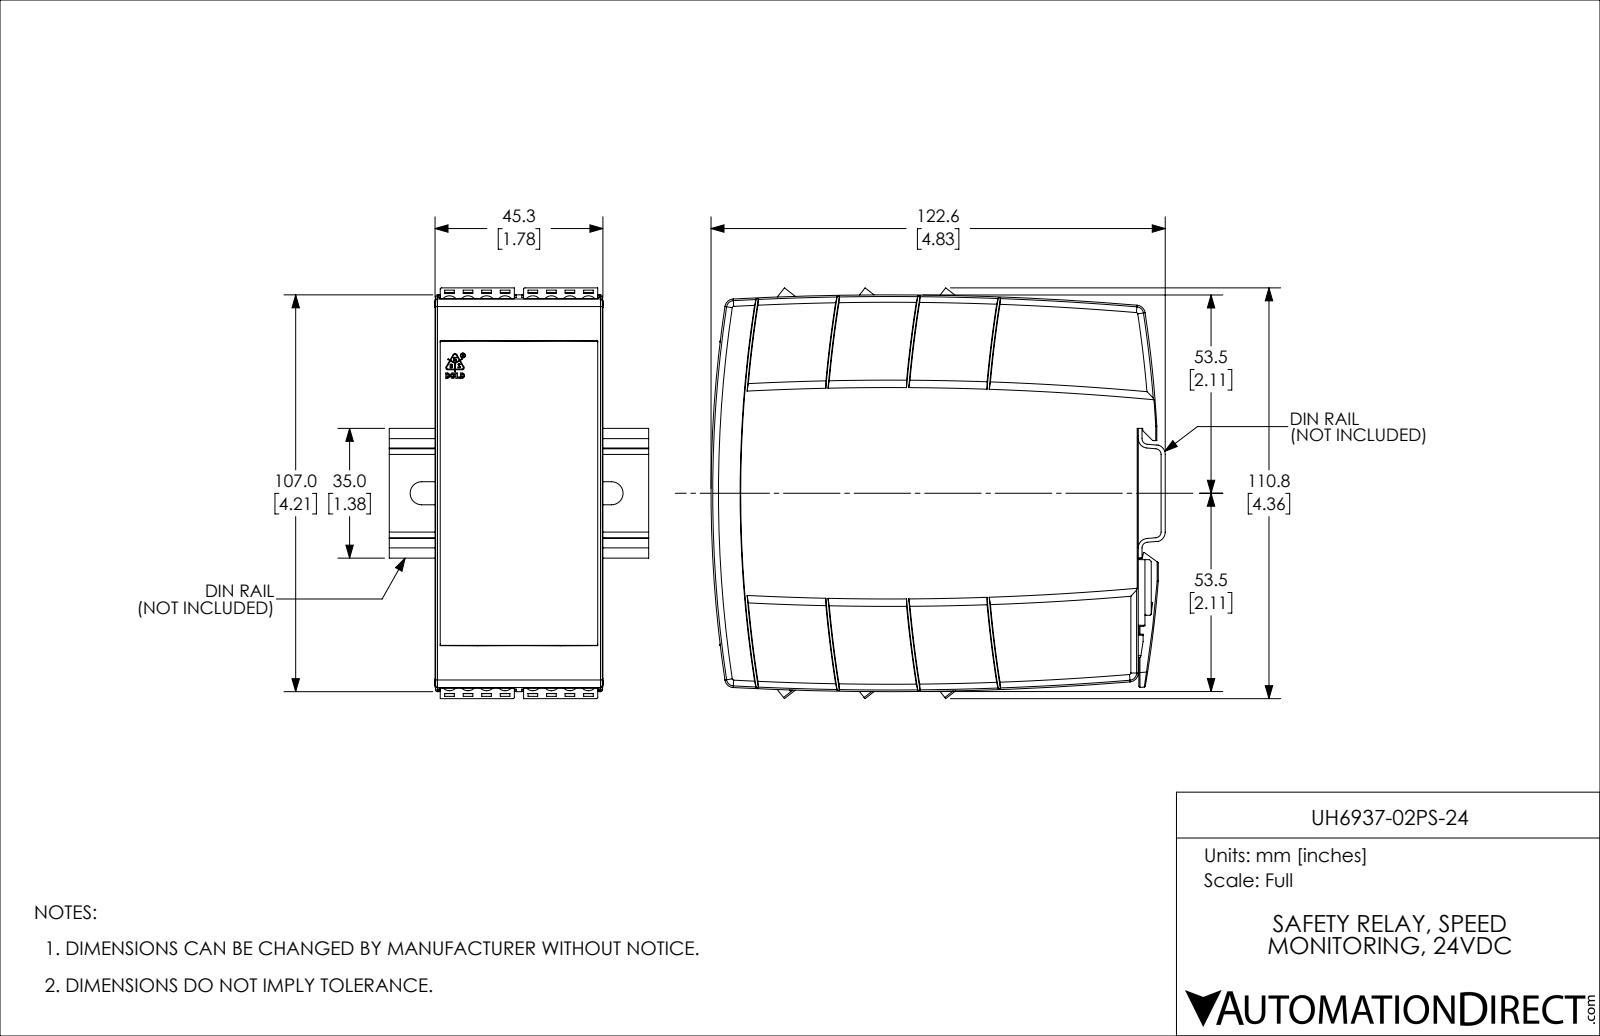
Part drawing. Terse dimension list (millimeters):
name: UH6937-02PS-24
written by: SolidWorks 2018 (AUTOMOTIVE_DESIGN)
unit: mm
bodies: 17 solids, 9587 faces (7538 planar, 1783 cylindrical, 266 other)
size: 120.7 × 110.8 × 45.3
volume: 108 100 mm³; area: 122 800 mm²
holes: 48× ⌀1.5, 48× ⌀3.2, 48× ⌀4, 6× ⌀0.7, 6× ⌀0.8, 1× ⌀1.2
bosses: 48× ⌀3.8, 6× ⌀2, 1× ⌀1.3
rounds: 48× R2.9, 37× R0.4, 18× R0.1, 18× R0.3, 18× R0.3, 18× R0.3, 12× R0.1, 12× R0.2
face distances: 1.1, 43.7, 42.6, 1.3, 43.9, 45.1, 17.1, 22.5, 44.9, 2
hole spacings: 5, 10, 22.5, 17.5, 27.5, 26.2, 12.5, 14.3
